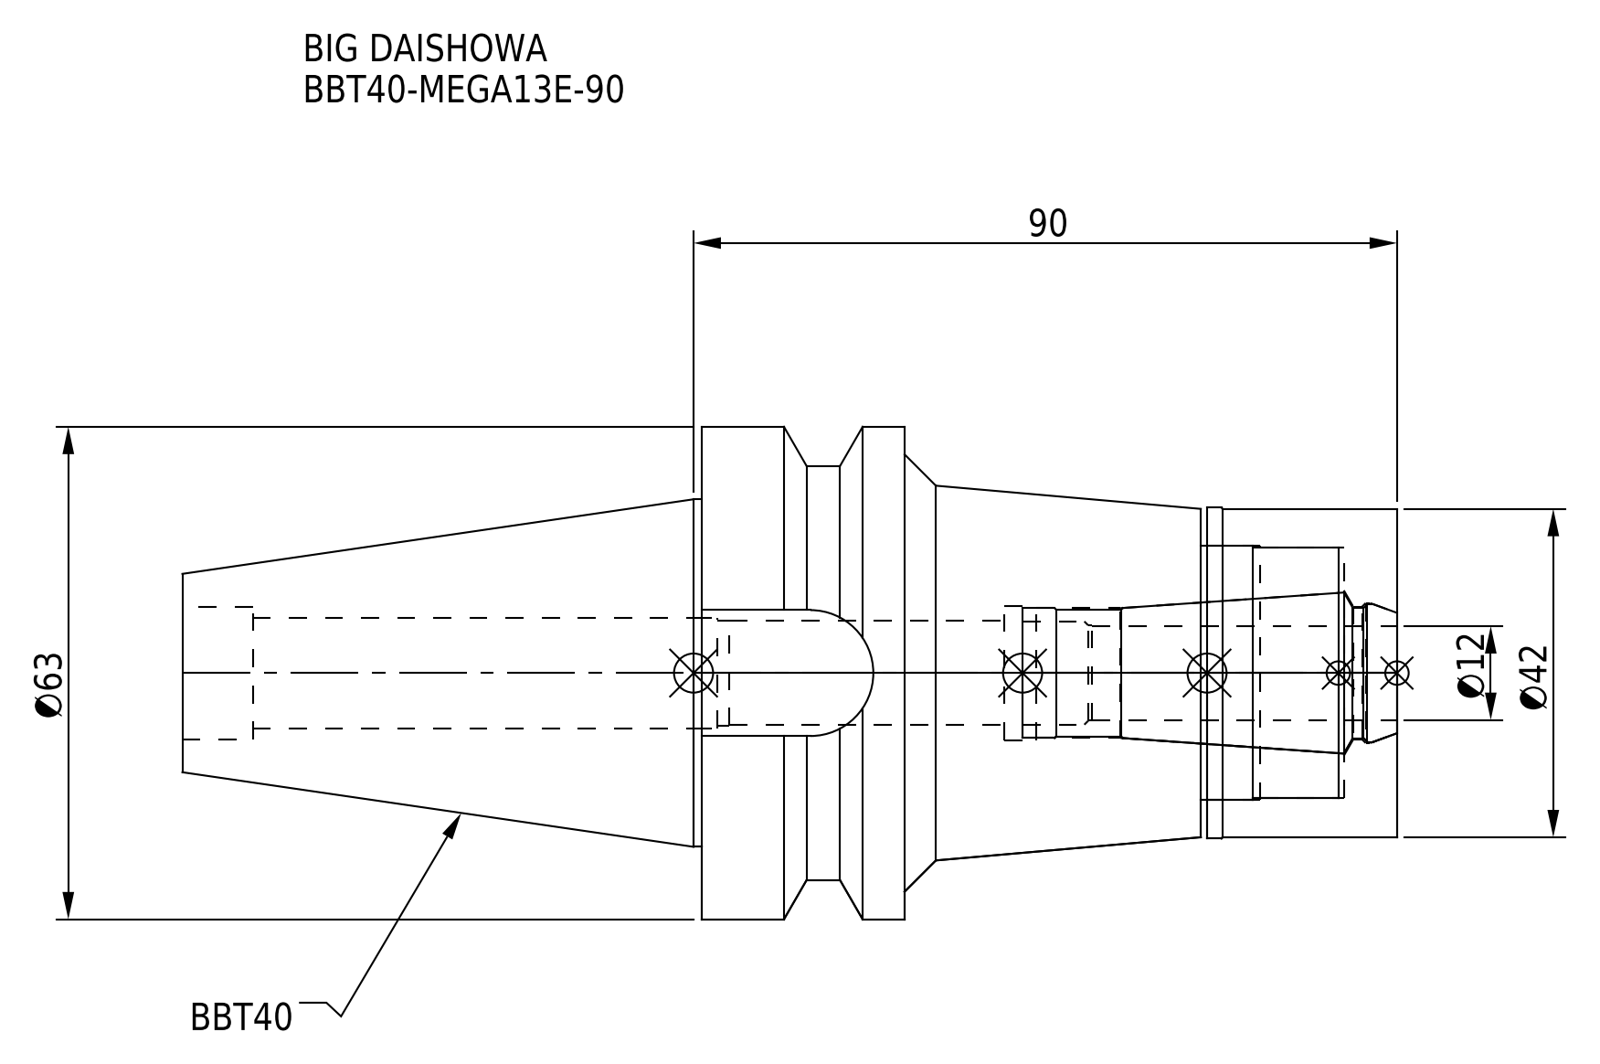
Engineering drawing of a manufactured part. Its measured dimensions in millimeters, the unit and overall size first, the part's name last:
Units: millimetres
Overall size (bounding box): 155.4 × 63 × 63
Round holes (diameter × count): ⌀13.3 ×1, ⌀13.5 ×1, ⌀14.2 ×1, ⌀16.6 ×1, ⌀17 ×1, ⌀17.2 ×1, ⌀17.9 ×1, ⌀32 ×1, ⌀32.5 ×1
Round bosses / shafts (diameter × count): ⌀63 ×1, ⌀53 ×1, ⌀44.45 ×1, ⌀42.3 ×1, ⌀42 ×1
Partial cylindrical surfaces — rounded edges, fillets, slot ends (radius × count): R8.05 ×1
Main face-to-face distances: 89, 63, 26, 25.1, 38.7, 24.3, 64.7, 0.8, 37.9, 63.9
Volume: 202 753 mm³ · Surface area: 39 671 mm²
Bodies: 2 solids, 81 faces (21 planar, 40 cylindrical, 20 other)
Part name (STEP PRODUCT): BBT40-MEGA13E-90_1.stp; BBT40-MEGA13E-90-120.stp; BBT40-MEGA13E-90; DXF_TEMP_ASSY_ASM_4_ASM.stp (+3 more)
STEP written by: SolidWorks 2019 (CONFIG_CONTROL_DESIGN)
